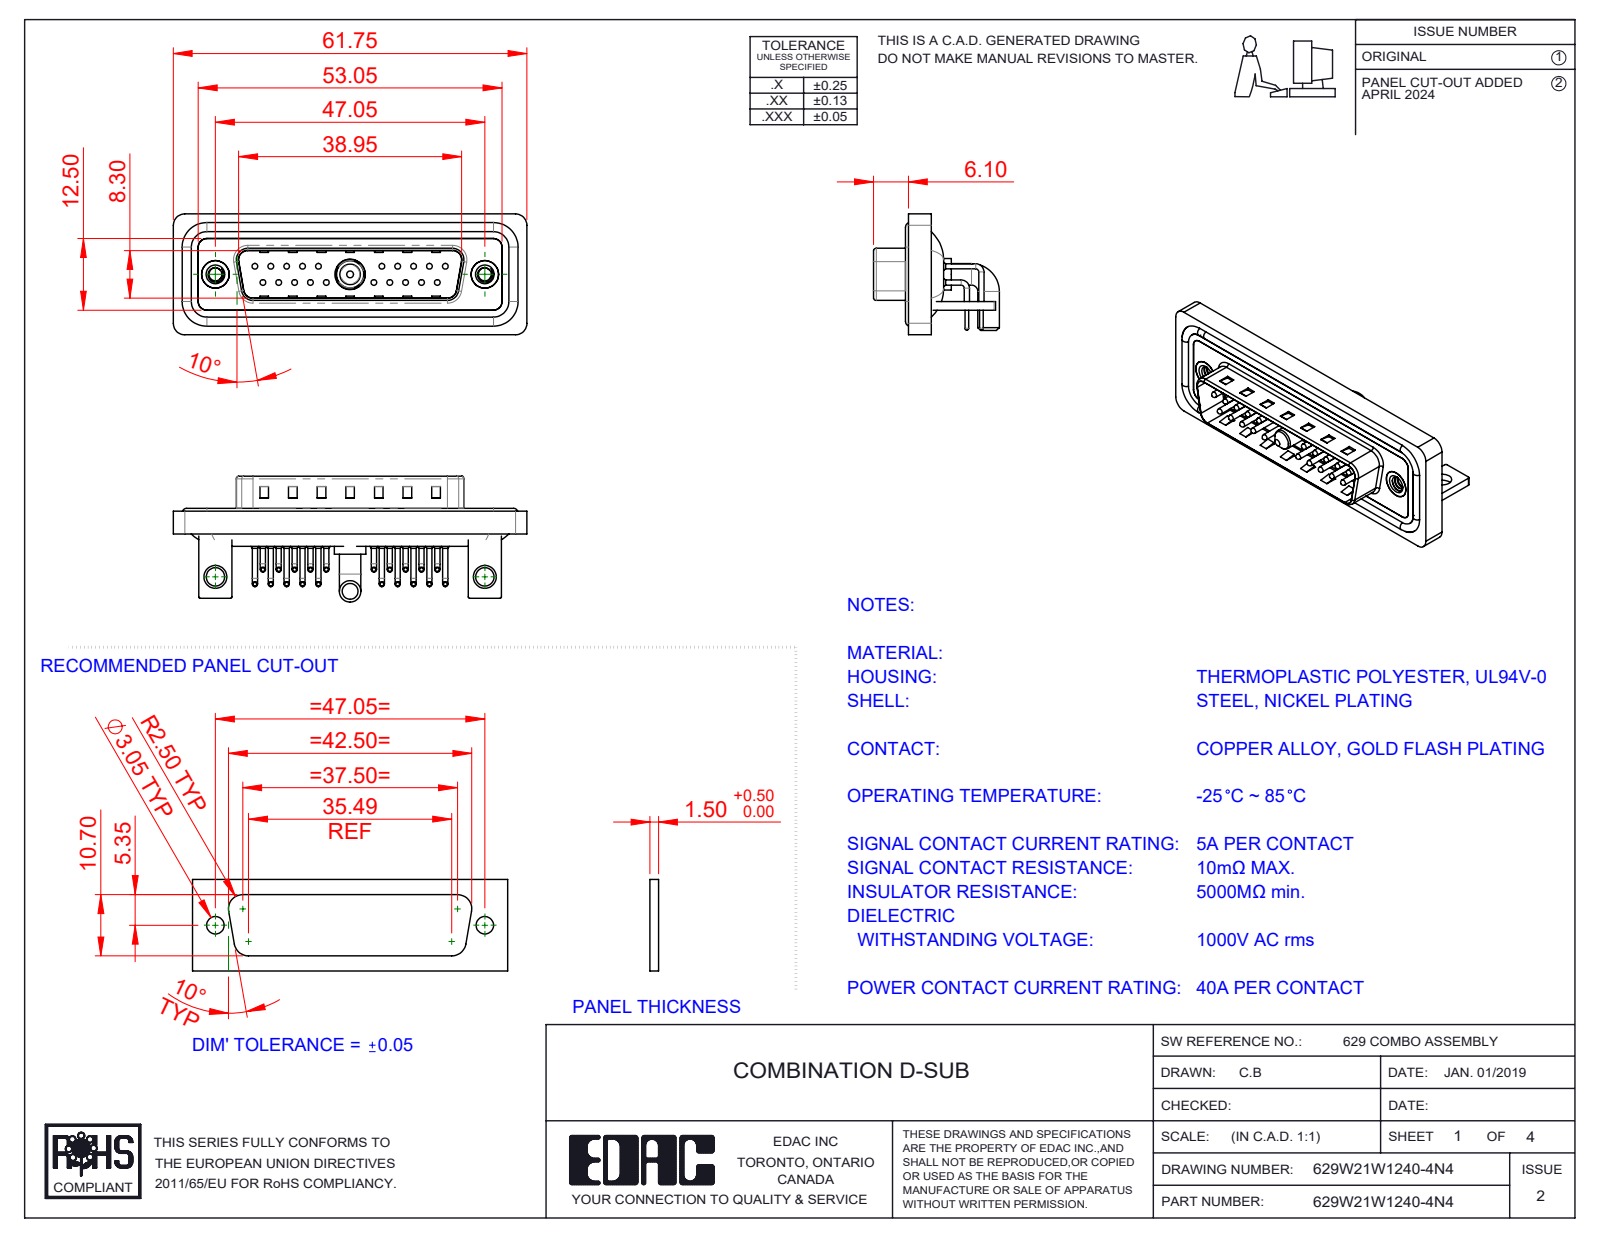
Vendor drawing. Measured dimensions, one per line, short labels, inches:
name: 629W21W1140-4N4; 629Combo Waterproof Housing_25 Contacts; Power Pin_40A RA; 629Combo Threaded Rivet_3 (+6 more)
written by: SolidWorks 2023 (CONFIG_CONTROL_DESIGN)
unit: in
bodies: 31 solids, 2766 faces (1519 planar, 947 cylindrical, 300 other)
size: 2.431 × 0.865 × 0.831
volume: 0.474 in³; area: 20.7 in²
holes: 20× ⌀0.03, 20× ⌀0.063, 20× ⌀0.079, 2× ⌀0.089, 2× ⌀0.126, 2× ⌀0.157, 2× ⌀0.189, 2× ⌀0.197, 1× ⌀0.191, 1× ⌀0.209
bosses: 40× ⌀0.035, 20× ⌀0.059, 20× ⌀0.039, 20× ⌀0.026, 4× ⌀0.063, 2× ⌀0.193, 2× ⌀0.148, 1× ⌀0.217
rounds: 20× R0.04, 19× R0.079, 18× R0.059, 16× R0.01, 9× R0.02, 8× R0.063, 4× R0.024, 4× R0.026
face distances: 0.016, 0.031, 0.083, 0.114, 0.059, 0.043, 0.161, 0.063, 0.177, 0.146
hole spacings: 0.124, 0.109, 0.218, 0.327, 0.198, 0.763, 0.826, 0.872
